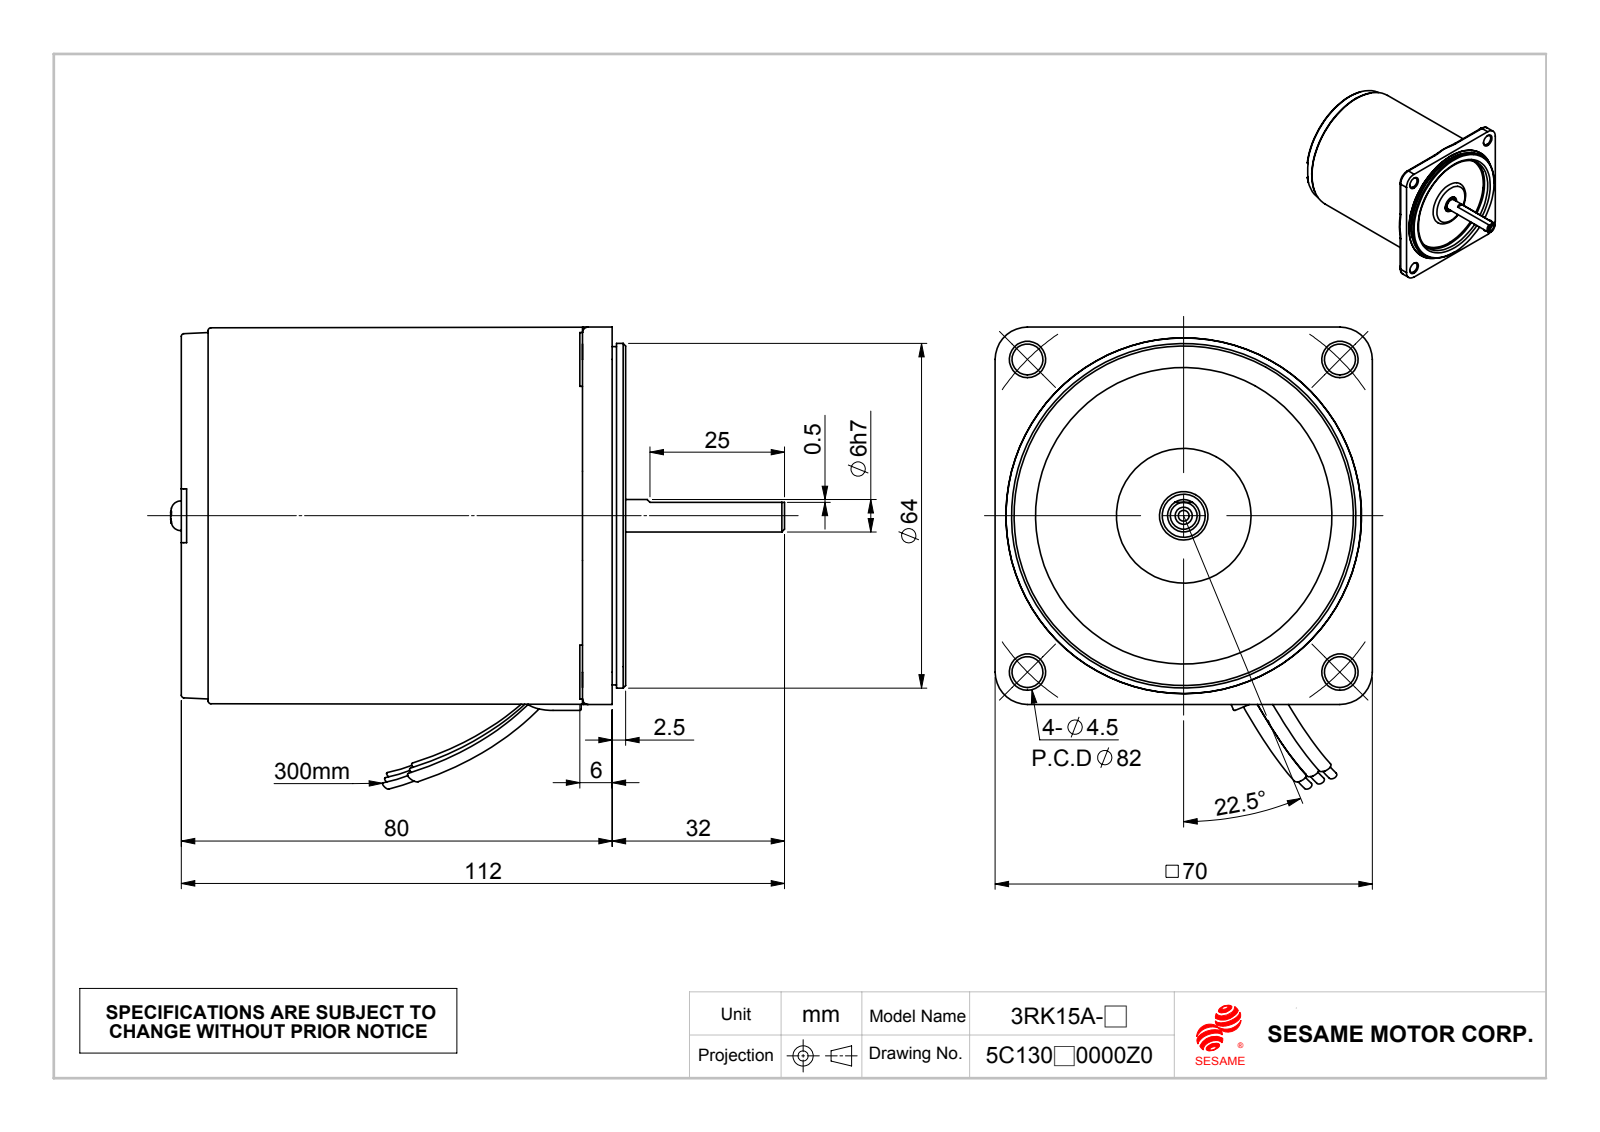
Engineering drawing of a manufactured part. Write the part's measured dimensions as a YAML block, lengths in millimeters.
part_name: "펥짰웰찿M3즤36x1t_Default; C364_車工(成品); 15A_0.成品; 線扣 (+1 more)"
step_written_by: "SolidWorks 2010 (CONFIG_CONTROL_DESIGN)"
units: millimeters
bodies: {solids: 10, faces: 323, planar: 110, cylindrical: 103, other: 110}
overall_size: [113.96, 85.72, 70]
volume: 313538
surface_area: 41900
round_holes:
  - {diameter: 5.75, count: 4}
  - {diameter: 2.5, count: 3}
  - {diameter: 4, count: 2}
  - {diameter: 2, count: 1}
  - {diameter: 7.2, count: 1}
  - {diameter: 9, count: 1}
  - {diameter: 9.5, count: 1}
  - {diameter: 18, count: 1}
  - {diameter: 55, count: 1}
  - {diameter: 58.2, count: 1}
  - {diameter: 66, count: 1}
round_bosses_or_shafts:
  - {diameter: 10, count: 4}
  - {diameter: 5.5, count: 2}
  - {diameter: 3, count: 2}
  - {diameter: 63.93, count: 1}
  - {diameter: 62.73, count: 1}
  - {diameter: 57.42, count: 1}
  - {diameter: 57.2, count: 1}
  - {diameter: 36, count: 1}
partial_cylinders:
  - {radius: 0.25, count: 8}
  - {radius: 0.3, count: 8}
  - {radius: 1, count: 4}
  - {radius: 6, count: 4}
  - {radius: 5.25, count: 1}
  - {radius: 33.91, count: 1}
face_to_face_distances: [77.4, 77.5, 75.89, 1.51, 1.61, 1.5, 79, 3.11, 1.6, 78.5]
hole_center_spacings: [14, 28, 32.65, 41.01, 51.87, 58, 32.56, 32.74]
